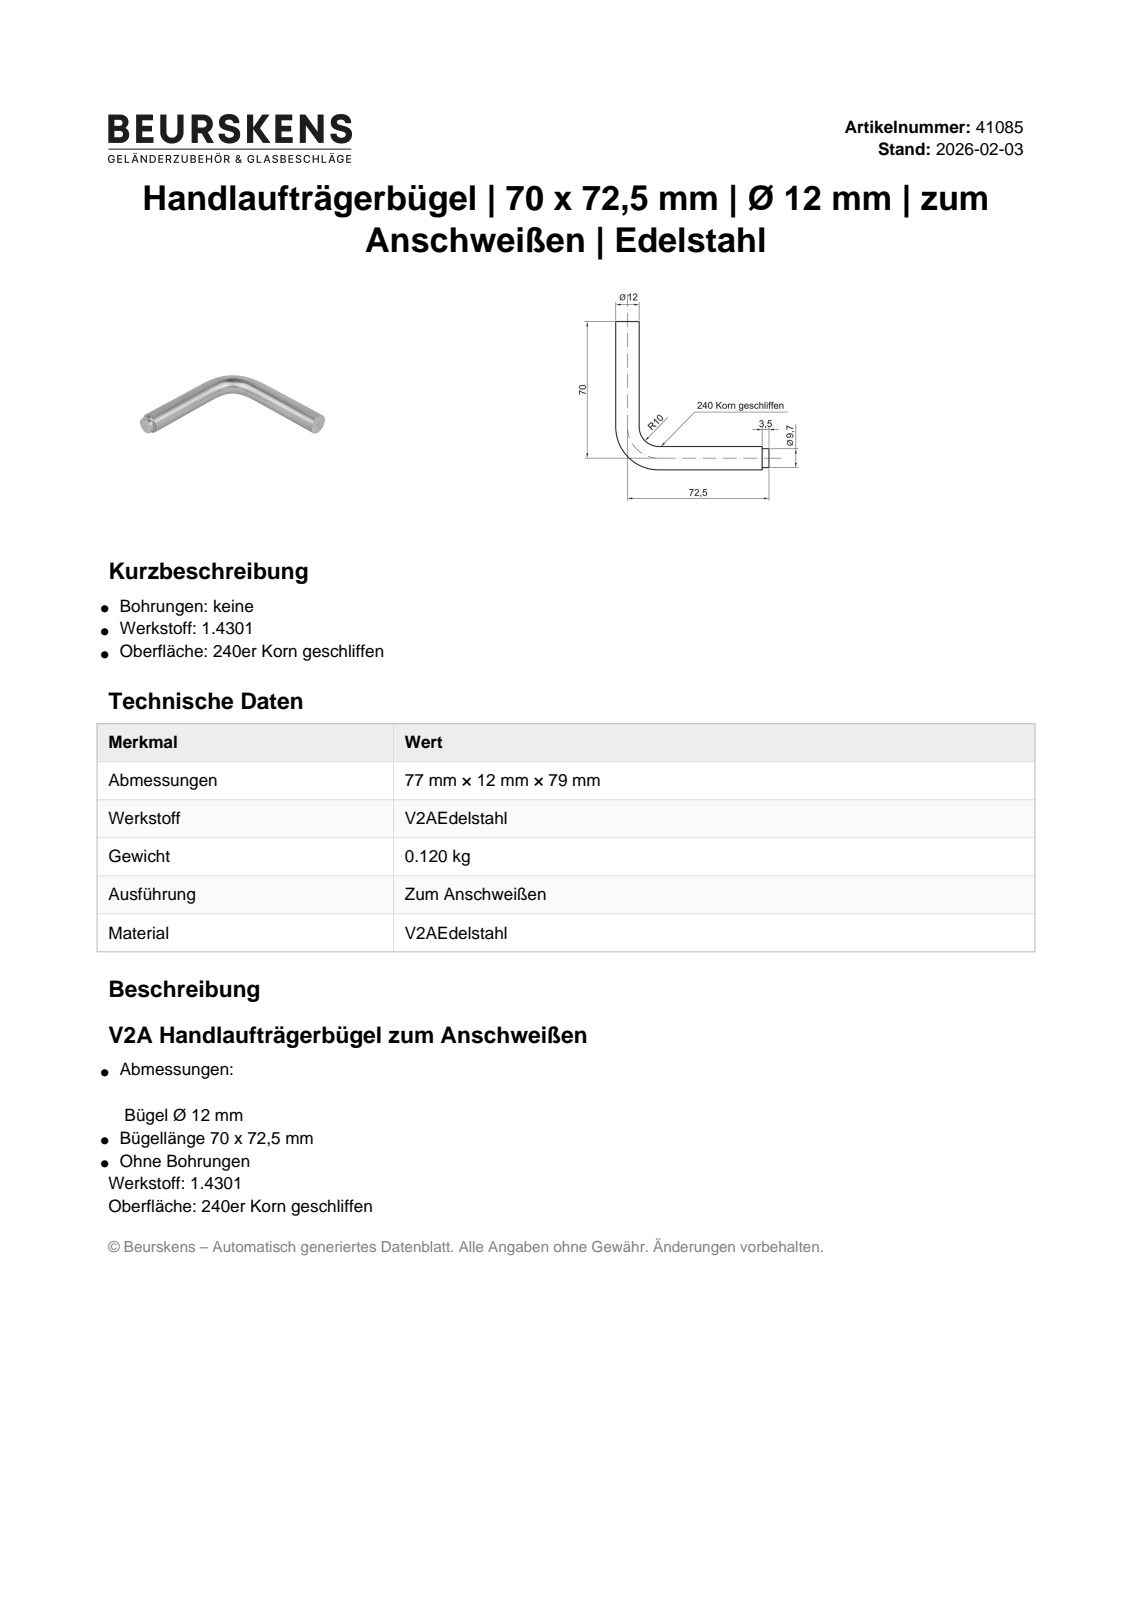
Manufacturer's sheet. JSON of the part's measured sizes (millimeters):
{"part_name": "41085", "step_written_by": "Autodesk Inventor 2022 (AUTOMOTIVE_DESIGN)", "units": "millimeters", "bodies": {"solids": 1, "faces": 5, "planar": 3, "cylindrical": 1, "other": 1}, "overall_size": [78.5, 76, 12], "volume_mm3": 15461, "surface_area_mm2": 5408, "round_bosses_or_shafts": [[9.7, 1]], "face_to_face_distances": [3.5]}
